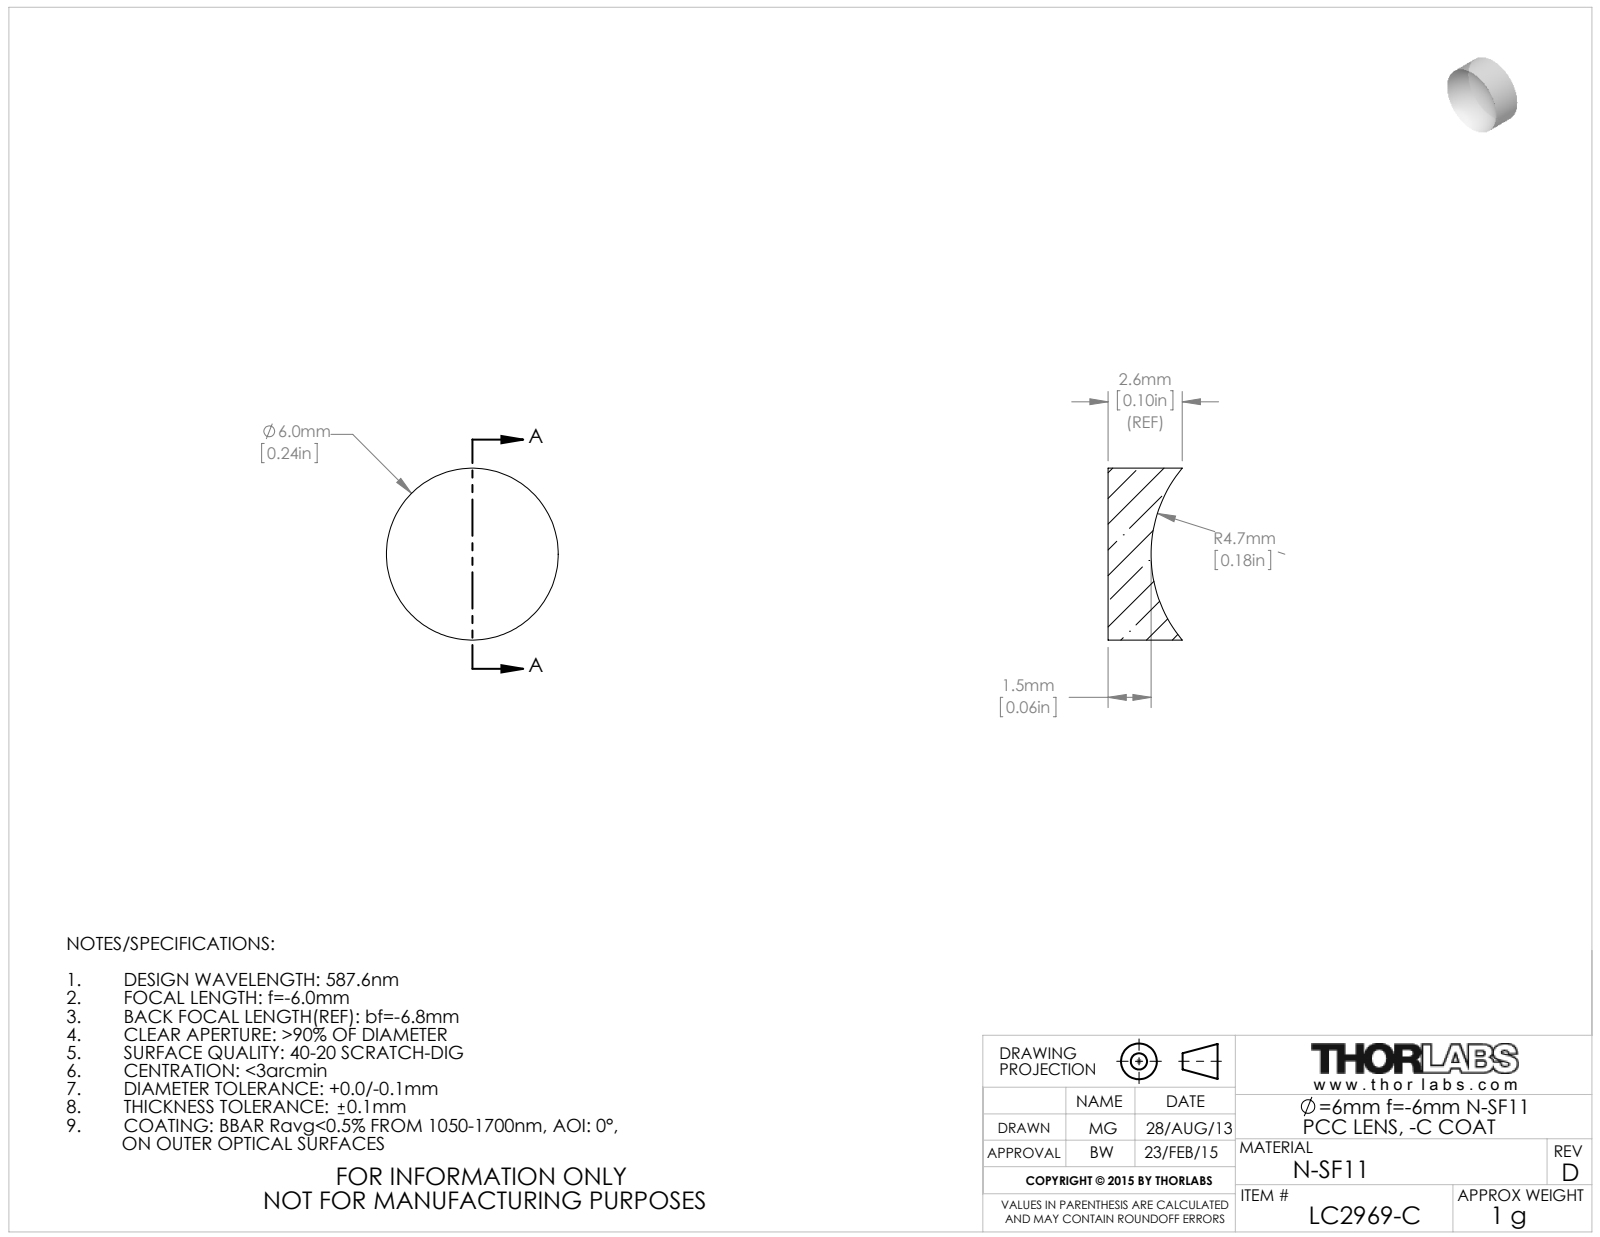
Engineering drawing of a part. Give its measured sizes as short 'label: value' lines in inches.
name: 5450-E0W
written by: SolidWorks 2014 (CONFIG_CONTROL_DESIGN)
unit: in
bodies: 1 solid, 5 faces (1 planar, 2 cylindrical, 2 other)
size: 0.236 × 0.236 × 0.102
volume: 0.003 in³; area: 0.169 in²
bosses: 1× ⌀0.236
